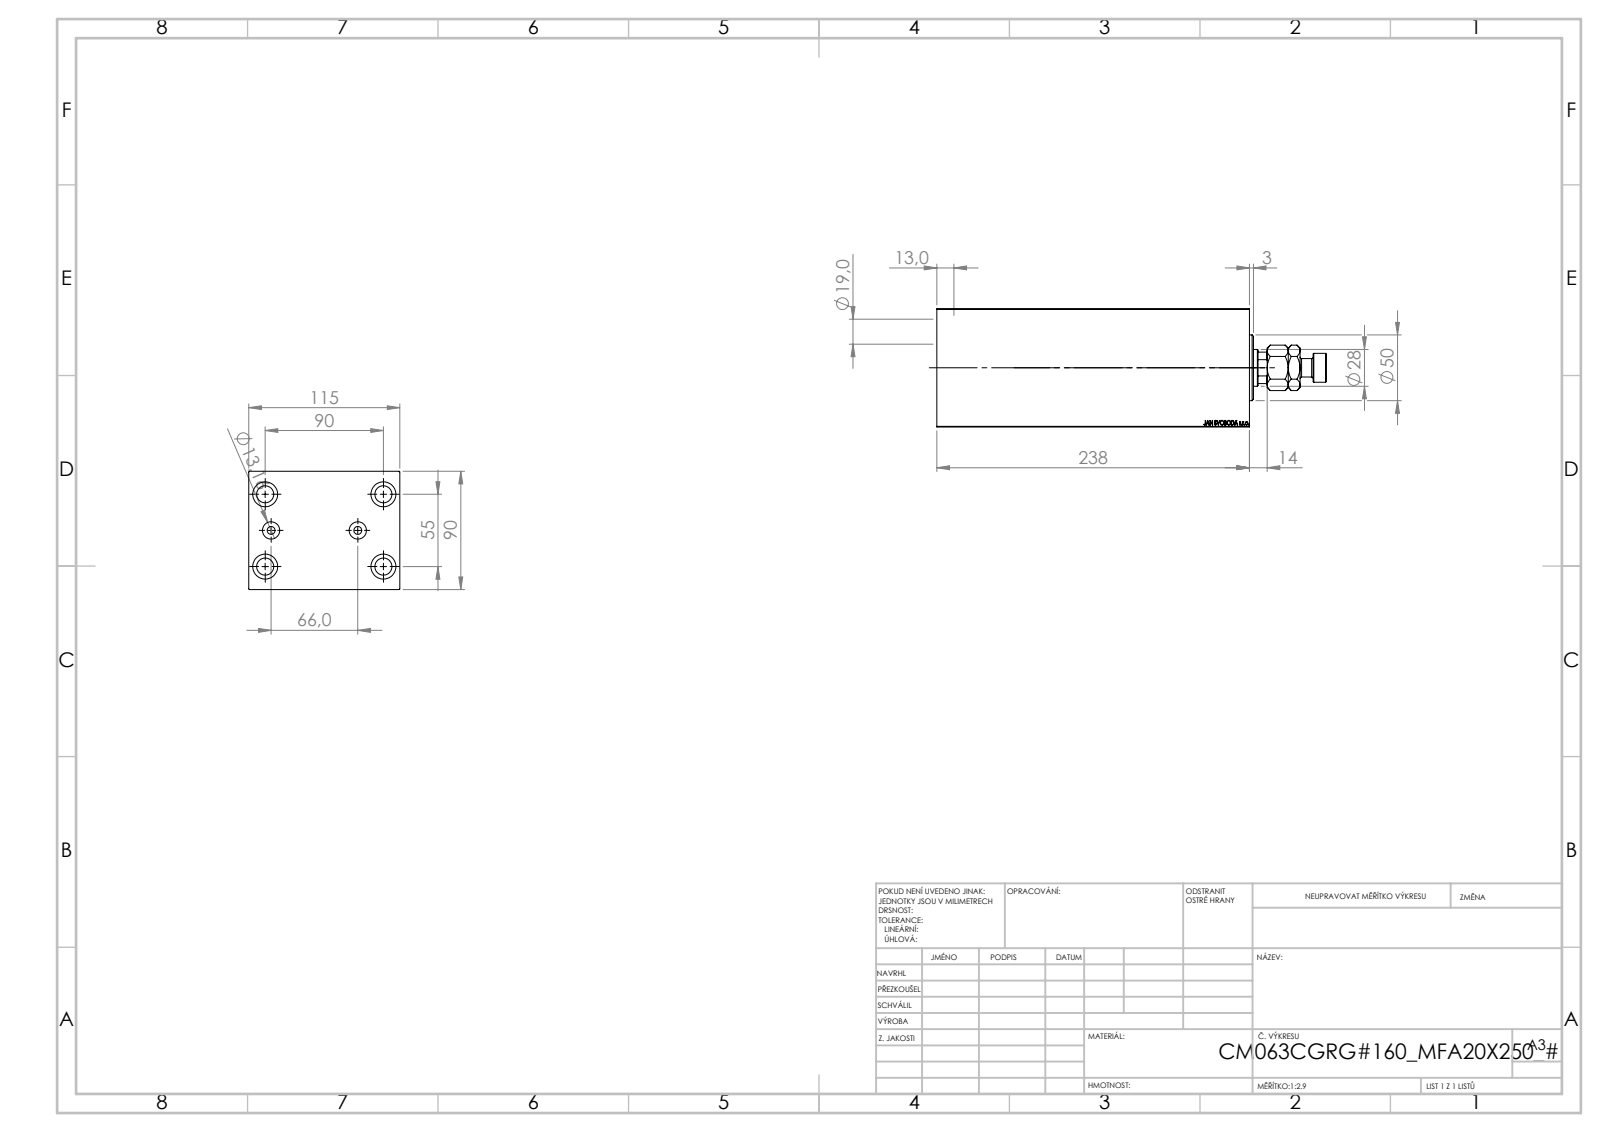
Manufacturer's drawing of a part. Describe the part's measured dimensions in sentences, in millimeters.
The part is named "MFA; V450CM_VC_B; V450CM_C_Body; V450CM_C_VCP". Its 3-D file was written by "SolidWorks 2019 (CONFIG_CONTROL_DESIGN)". It is 4 solids with 913 faces: 425 planar, 62 cylindrical and 426 other. Overall it measures 296.5 by 115 by 90 millimeters. Its volume is 1 937 000 cubic millimeters and its surface area 259 419 square millimeters. Round holes: 4 of diameter 13, 4 of diameter 19, 2 of diameter 6, 2 of diameter 13.16, 1 of diameter 18.5, 1 of diameter 28, 1 of diameter 31.5, 1 of diameter 63, 1 of diameter 65, 1 of diameter 72. Round bosses or shafts: 1 of diameter 50, 1 of diameter 22, 1 of diameter 14. Partial cylindrical surfaces (rounded edges, fillets, slot ends): 1 of radius 13.5. The main face-to-face distances are 90, 115, 238, 17.5, 220.5, 29.3, 191.2, 208.7, 189.3, 160. The hole center spacings are 30, 52.74, 82.71, 33, 55, 90, 105.48, 66.
